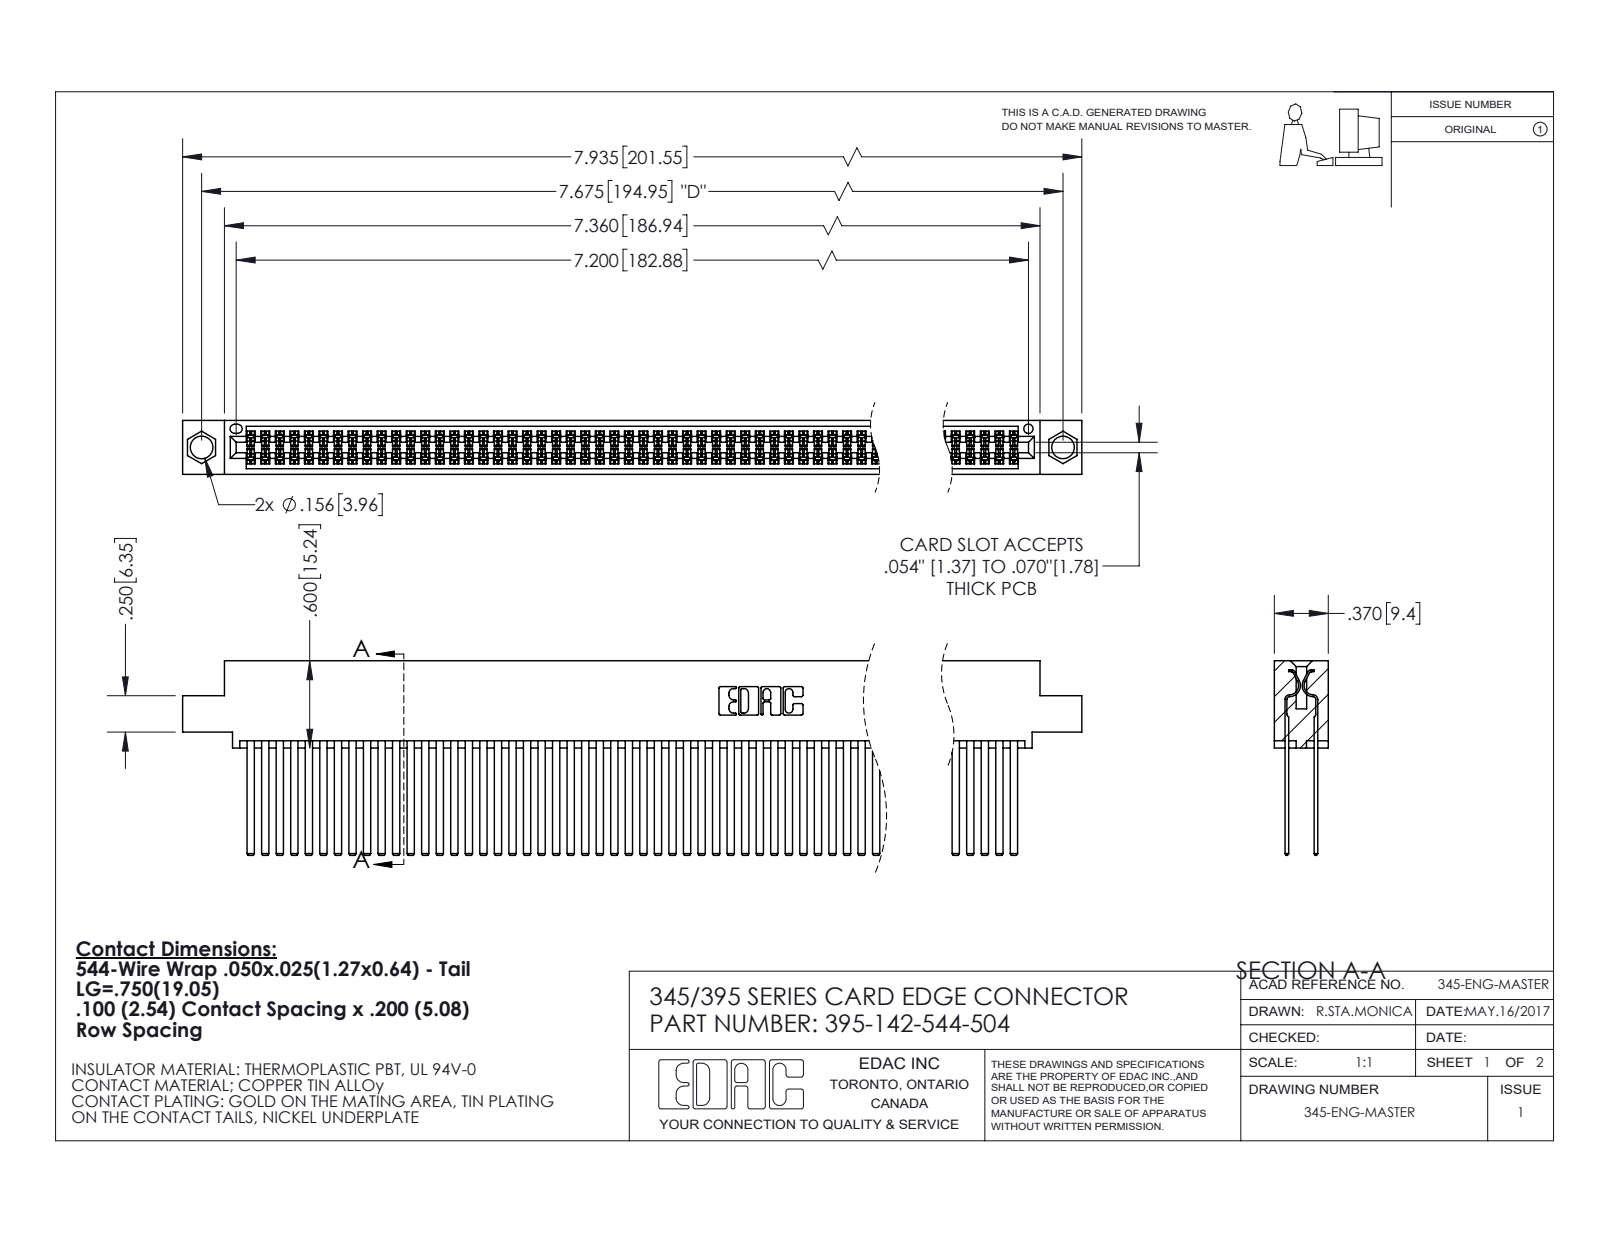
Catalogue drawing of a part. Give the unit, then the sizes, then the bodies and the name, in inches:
Units: inches
Overall size (bounding box): 7.935 × 1.337 × 0.37
Round holes (diameter × count): ⌀0.156 ×2, ⌀0.064 ×1
Partial cylindrical surfaces — rounded edges, fillets, slot ends (radius × count): R0.006 ×213, R0.01 ×22, R0.007 ×6, R0.031 ×6, R0.026 ×3, R0.014 ×2, R0.019 ×2, R0.022 ×2
Main face-to-face distances: 0.2, 0.025, 0.298, 0.072, 0.098, 0.272, 0.225, 0.175, 0.37, 0.149
Hole centre spacings: 0.27, 7.439, 7.675
Volume: 1.322 in³ · Surface area: 59.45 in²
Bodies: 143 solids, 6392 faces (4216 planar, 2176 cylindrical, 0 other)
Part name (STEP PRODUCT): 345 Part_0.110 Offset - 0.156 Dia-TI; 395-142-544-504; 345-292-001_345-293-144
STEP written by: SolidWorks 2020 (CONFIG_CONTROL_DESIGN)
